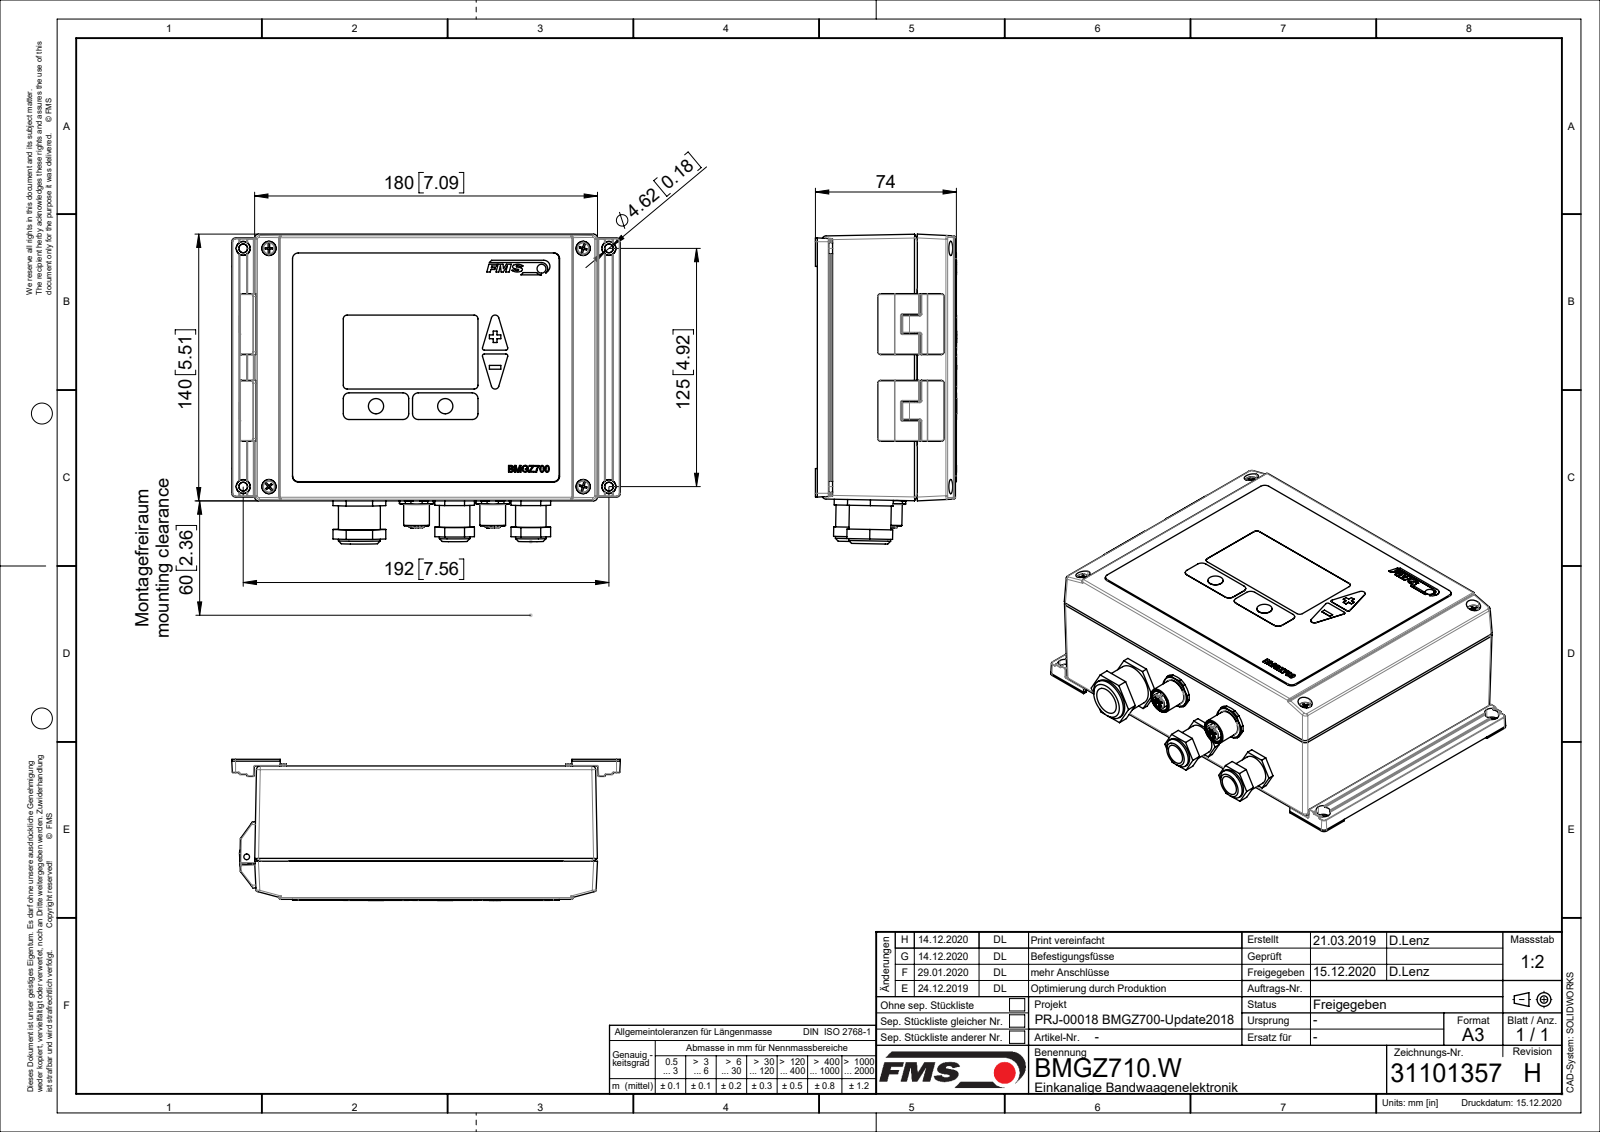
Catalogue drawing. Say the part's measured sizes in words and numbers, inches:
The part is named "31103331_01; 31100824_M16x1.5 kurz; 31102324_vereinfacht_01; 31100824_M20x1.5 kurz (+8 more)". Its 3-D file was written by "SolidWorks 2018 (CONFIG_CONTROL_DESIGN)". It is 74 solids with 14912 faces: 8641 planar, 4138 cylindrical and 2133 other. Overall it measures 8.031 by 6.077 by 2.917 inches. Its volume is 29.18 cubic inches and its surface area 601.8 square inches. Round holes: 32 of diameter 0.039, 32 of diameter 0.039, 18 of diameter 0.047, 17 of diameter 0.055, 10 of diameter 0.043, 10 of diameter 0.13, 8 of diameter 0.094, 8 of diameter 0.177, 8 of diameter 0.236, 8 of diameter 0.315, 5 of diameter 0.571, 4 of diameter 0.128. Round bosses or shafts: 60 of diameter 0.024, 16 of diameter 0.217, 12 of diameter 0.025, 11 of diameter 0.079, 9 of diameter 0.118, 8 of diameter 0.157, 8 of diameter 0.055, 4 of diameter 0.276. Partial cylindrical surfaces (rounded edges, fillets, slot ends): 596 of radius 0.008, 476 of radius 0.012, 289 of radius 0.004, 271 of radius 0.02, 230 of radius 0.039, 72 of radius 0.018, 49 of radius 0.006, 40 of radius 0.01. The main face-to-face distances are 0.35, 0.118, 2.362, 2.713, 2.638, 0.276, 2.244, 2.594, 0.079, 0.075. The hole center spacings are 0.827, 1.791, 0.098, 0.965, 2.618, 1.113, 1.575, 0.197.
